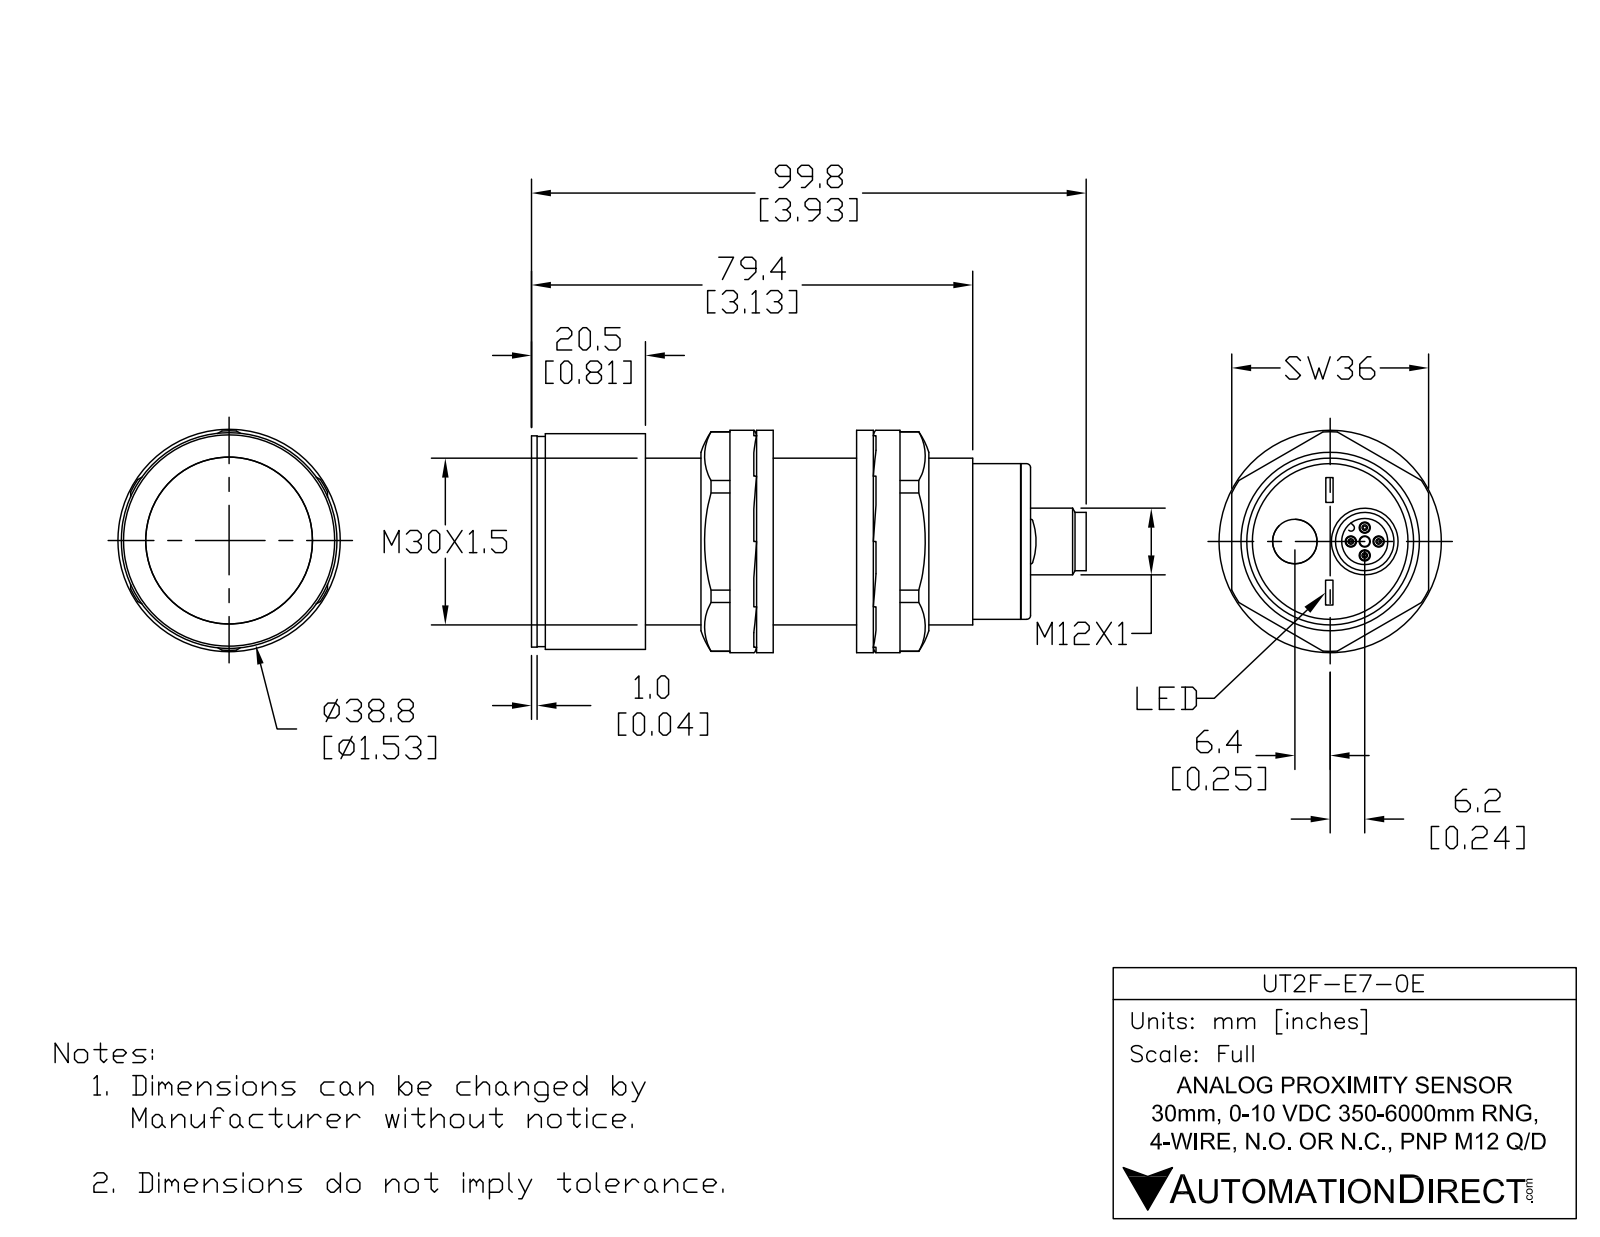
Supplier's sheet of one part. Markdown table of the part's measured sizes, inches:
| quantity | value |
| --- | --- |
| part name | UT2F-E7-0E |
| STEP written by | SolidWorks 2017 (AUTOMOTIVE_DESIGN) |
| units | inches |
| bodies | 5 solids, 108 faces (31 planar, 47 cylindrical, 30 other) |
| overall size | 3.894 × 1.528 × 1.528 |
| volume | 4.372 in³ |
| surface area | 24.88 in² |
| round holes (diameter × count) | 0.071 × 4, 0.315 × 1, 0.327 × 1, 0.372 × 1, 1.299 × 1 |
| round bosses / shafts (diameter × count) | 0.039 × 4, 1.528 × 1, 1.488 × 1, 1.181 × 1, 1.102 × 1, 0.472 × 1, 0.413 × 1, 0.364 × 1 |
| partial cylindrical surfaces (radius × count) | 0.012 × 2, 0.024 × 1 |
| main face-to-face distances | 3.37, 0.059, 3.429, 0.767, 0.709, 2.661, 0.059, 3.429, 0.071, 3.5 |
| hole center spacings | 0.098, 0.139, 0.197, 0.264, 0.505, 0.146, 0.245, 0.25 |
